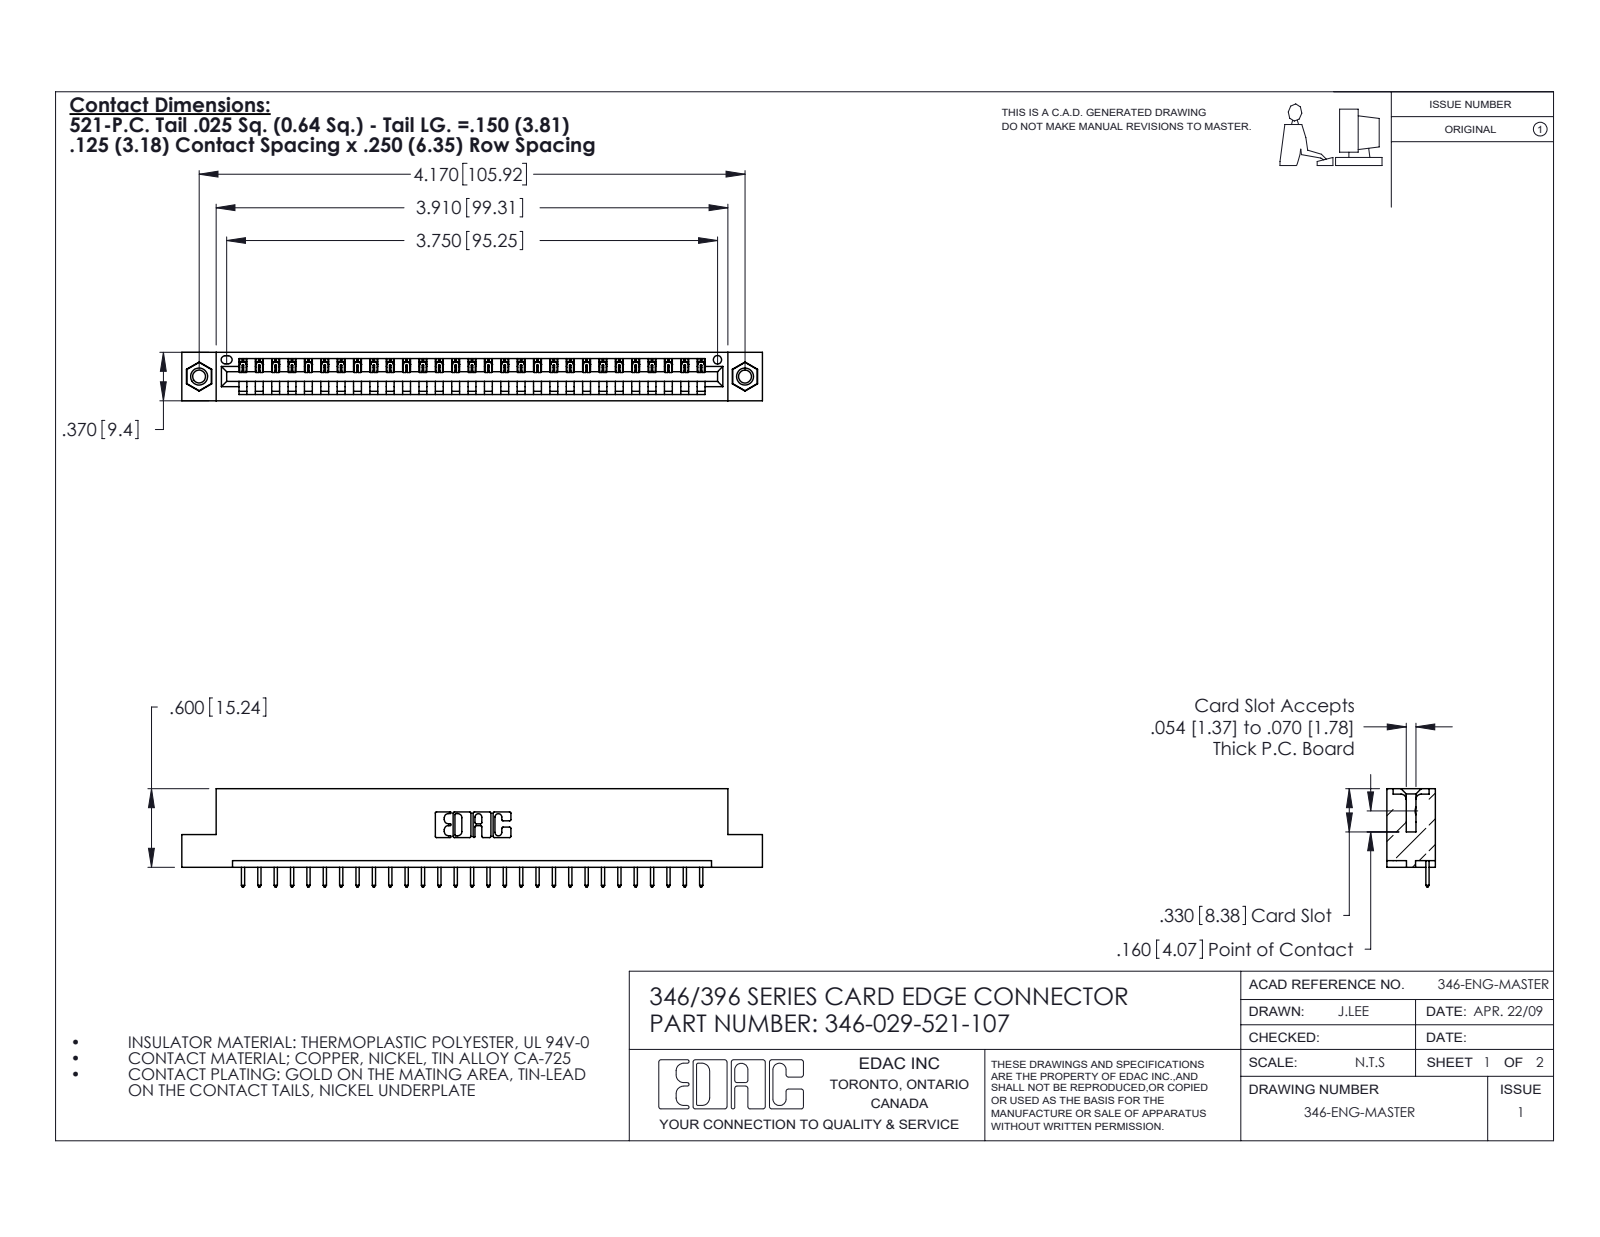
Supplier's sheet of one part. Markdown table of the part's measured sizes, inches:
| quantity | value |
| --- | --- |
| part name | 346 Part_Flush Mounting Lugs - 0.156 Dia-TI; 346-029-521-107; 345-292-001_345-293-121; 345-250-001_345-250-005-103 |
| STEP written by | SolidWorks 2020 (CONFIG_CONTROL_DESIGN) |
| units | inches |
| bodies | 32 solids, 1864 faces (1268 planar, 580 cylindrical, 16 other) |
| overall size | 4.435 × 0.75 × 0.37 |
| volume | 0.647 in³ |
| surface area | 19.86 in² |
| round holes (diameter × count) | 0.098 × 2, 0.125 × 2, 0.156 × 2, 0.064 × 1 |
| round bosses / shafts (diameter × count) | 0.155 × 2 |
| partial cylindrical surfaces (radius × count) | 0.006 × 58, 0.01 × 58, 0.01 × 22, 0.007 × 6, 0.031 × 6, 0.026 × 3, 0.031 × 2, 0.04 × 2 |
| main face-to-face distances | 0.048, 0.322, 0.37, 0.25, 0.072, 0.298, 0.025, 0.148, 0.222, 0.1 |
| hole center spacings | 0.246, 3.962, 4.17 |
